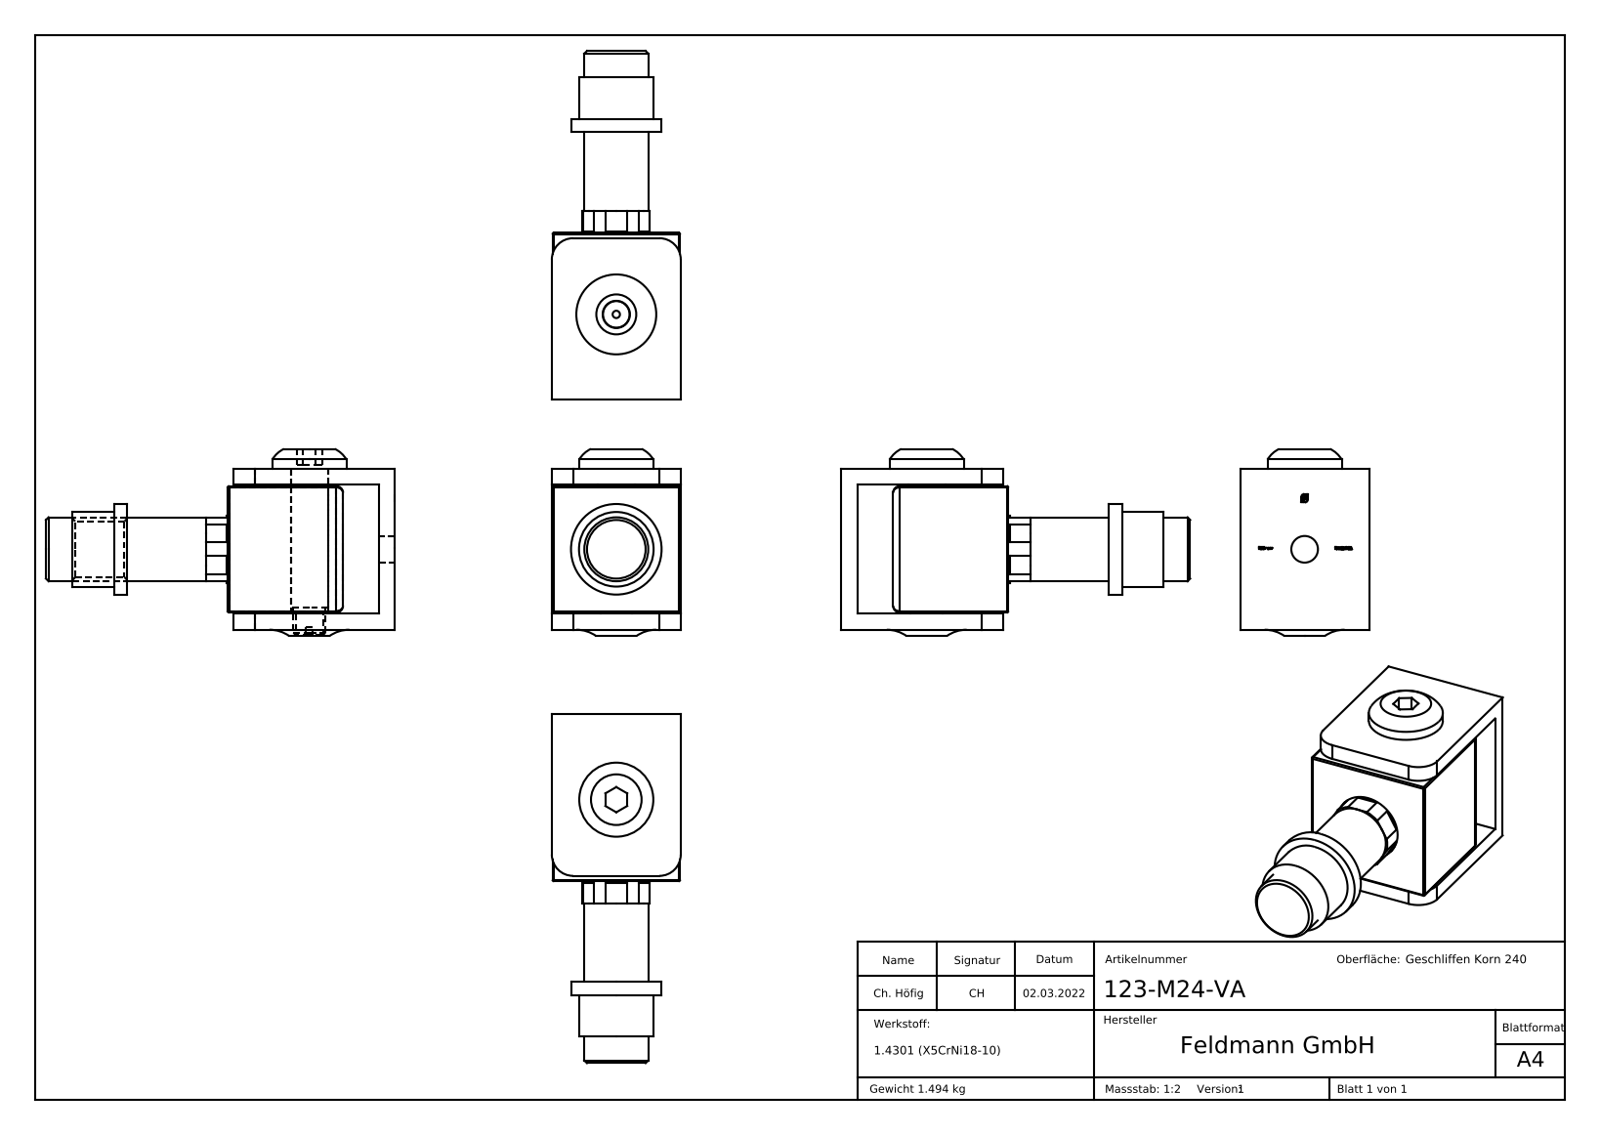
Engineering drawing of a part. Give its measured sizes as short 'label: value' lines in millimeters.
name: 123-MXX-VA Teil4_123-M24-VA Teil4; 123-MXX-VA Teil3_123-M24-VA Teil3; 123-MXX-VA Teil2_123-M24-VA Teil2; 123-MXX-VA Teil1_123-M24-VA Teil1 (+1 more)
written by: SolidWorks 2018 (CONFIG_CONTROL_DESIGN)
unit: mm
bodies: 4 solids, 366 faces (227 planar, 29 cylindrical, 110 other)
size: 130.9 × 70.3 × 48.4
volume: 189 133 mm³; area: 47 203 mm²
holes: 1× ⌀2.75, 1× ⌀10, 1× ⌀10.2, 1× ⌀14, 1× ⌀14.1, 1× ⌀21
bosses: 1× ⌀34, 1× ⌀28, 1× ⌀27.8, 1× ⌀25.3, 1× ⌀24, 1× ⌀12
rounds: 8× R0.5, 4× R2.5, 2× R8
face distances: 6, 54.4, 6.45, 53.95, 0.45, 47.95, 48.4, 60.4, 47.9, 48.15
